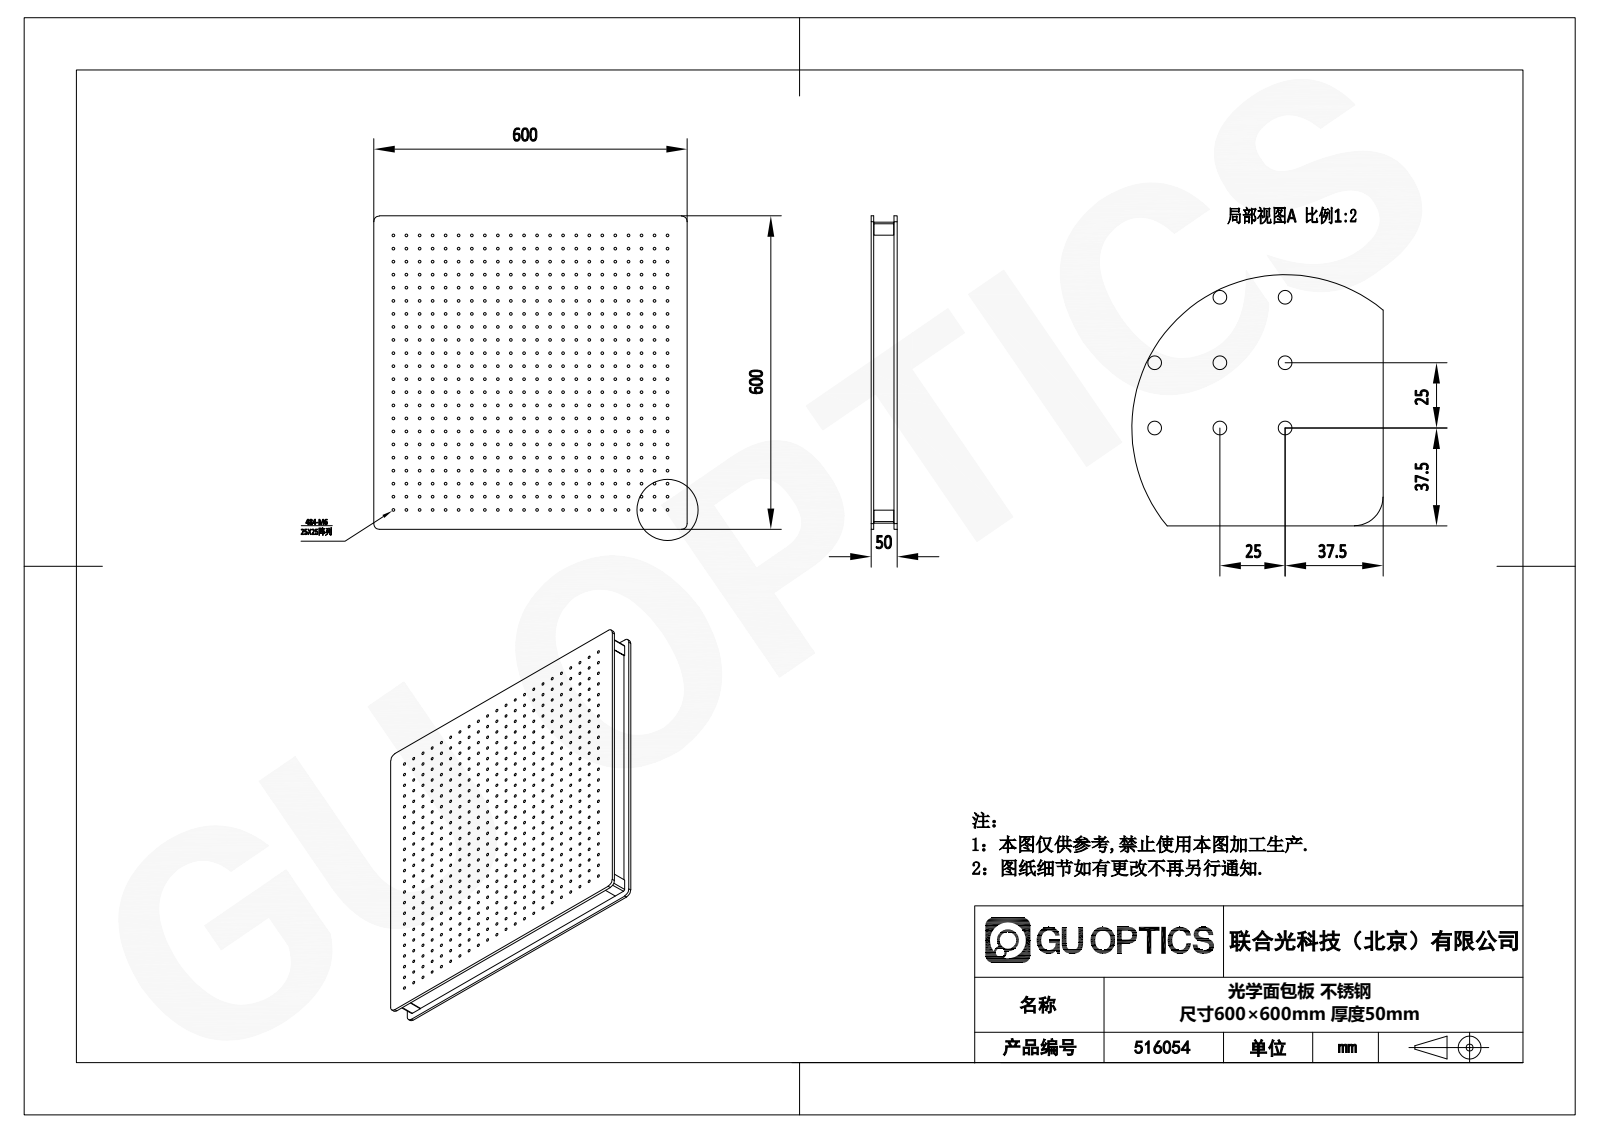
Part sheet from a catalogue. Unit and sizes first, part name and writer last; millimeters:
Units: millimetres
Overall size (bounding box): 600 × 600 × 50
Round holes (diameter × count): ⌀5.3 ×484
Partial cylindrical surfaces — rounded edges, fillets, slot ends (radius × count): R2 ×4, R3 ×4, R11 ×4
Main face-to-face distances: 50, 574, 6, 44, 45, 39, 5, 13, 587, 600
Hole centre spacings: 55.9, 25, 35.36, 50, 79.06, 103.08, 75, 127.48
Volume: 16 750 000 mm³ · Surface area: 952 938 mm²
Bodies: 1 solid, 1512 faces (528 planar, 984 cylindrical, 0 other)
Part name (STEP PRODUCT): 516054
STEP written by: SolidWorks 2020 (CONFIG_CONTROL_DESIGN)
